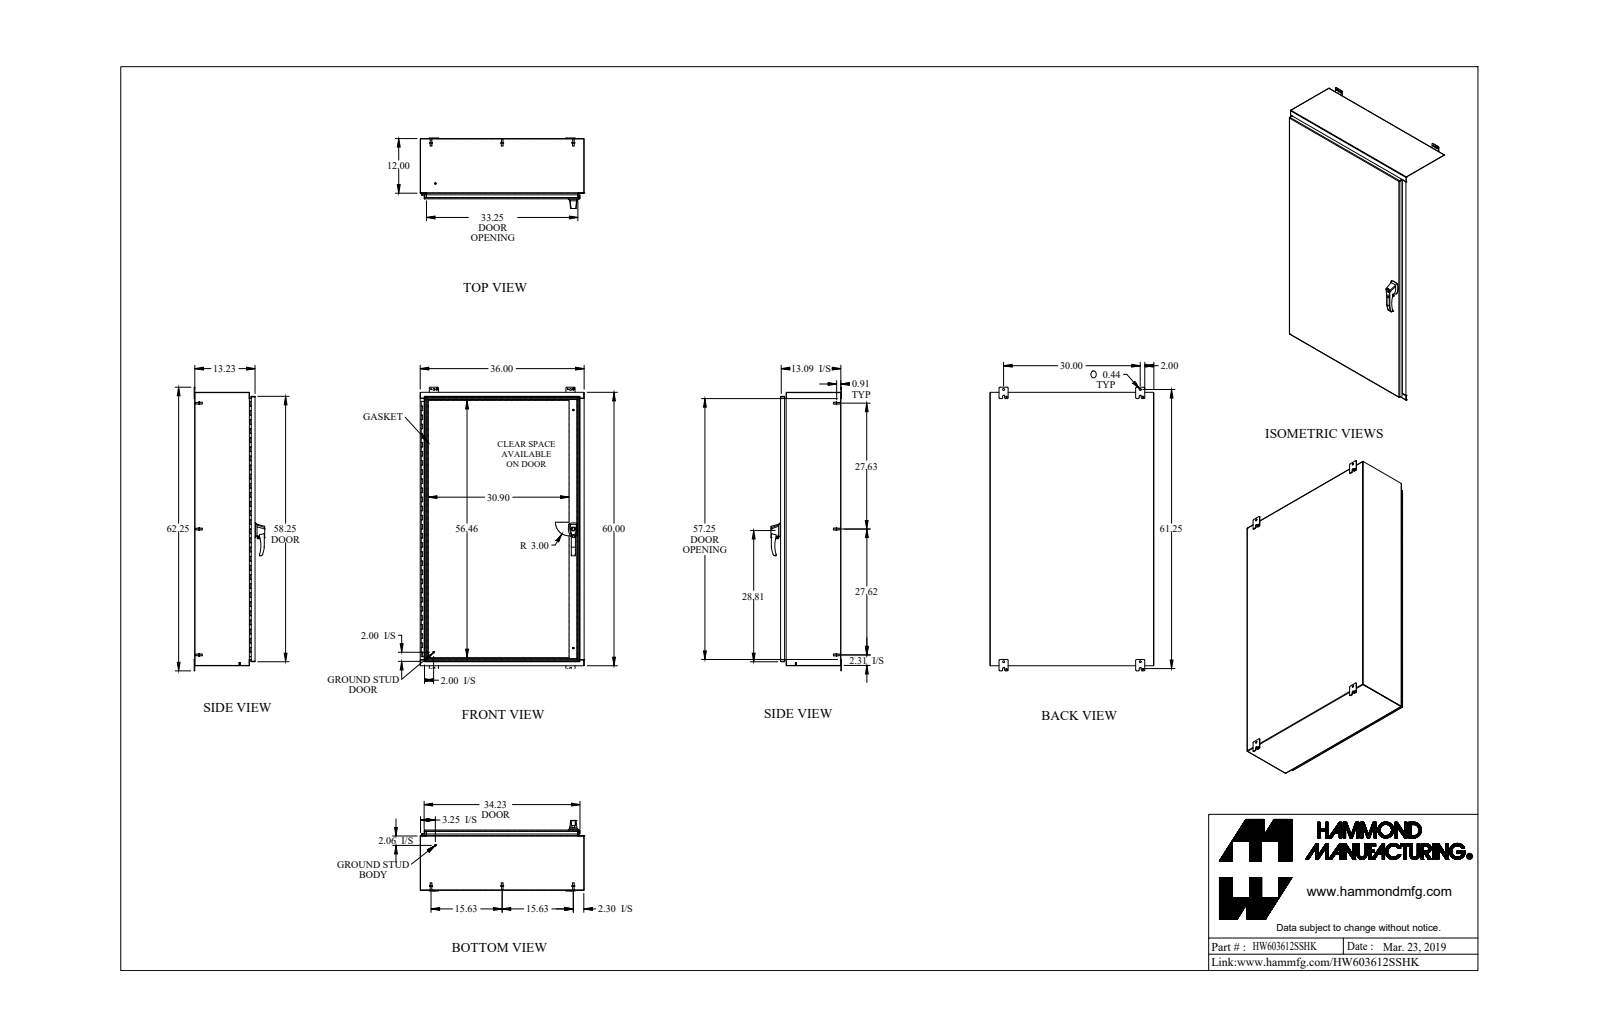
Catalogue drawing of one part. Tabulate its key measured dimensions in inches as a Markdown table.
| quantity | value |
| --- | --- |
| part name | HW603612SSHK |
| STEP written by | SolidWorks 2018 (AUTOMOTIVE_DESIGN) |
| units | inches |
| bodies | 48 solids, 1700 faces (809 planar, 753 cylindrical, 138 other) |
| overall size | 62.25 × 36 × 15.473 |
| volume | 610.5 in³ |
| surface area | 15 155 in² |
| round holes (diameter × count) | 0.176 × 6, 0.313 × 5, 0.25 × 3, 0.265 × 3, 0.413 × 3, 0.196 × 2, 0.256 × 2, 0.394 × 2, 0.437 × 2, 0.187 × 1, 0.233 × 1, 0.33 × 1 |
| round bosses / shafts (diameter × count) | 0.375 × 13, 0.65 × 8, 0.332 × 8, 0.25 × 7, 0.156 × 6, 0.313 × 4, 1 × 3, 0.51 × 3 |
| partial cylindrical surfaces (radius × count) | 0.25 × 27, 0.188 × 24, 0.036 × 14, 0.108 × 14, 0.06 × 12, 0.125 × 9, 0.218 × 8, 0.03 × 6 |
| main face-to-face distances | 0.072, 0.072, 13.066, 13.138, 0.095, 13.233, 13.161, 35.928, 59.928, 35.856 |
| hole center spacings | 1.111, 26.118, 26.119, 52.237, 1.338, 18.556, 24.78, 25.545 |
